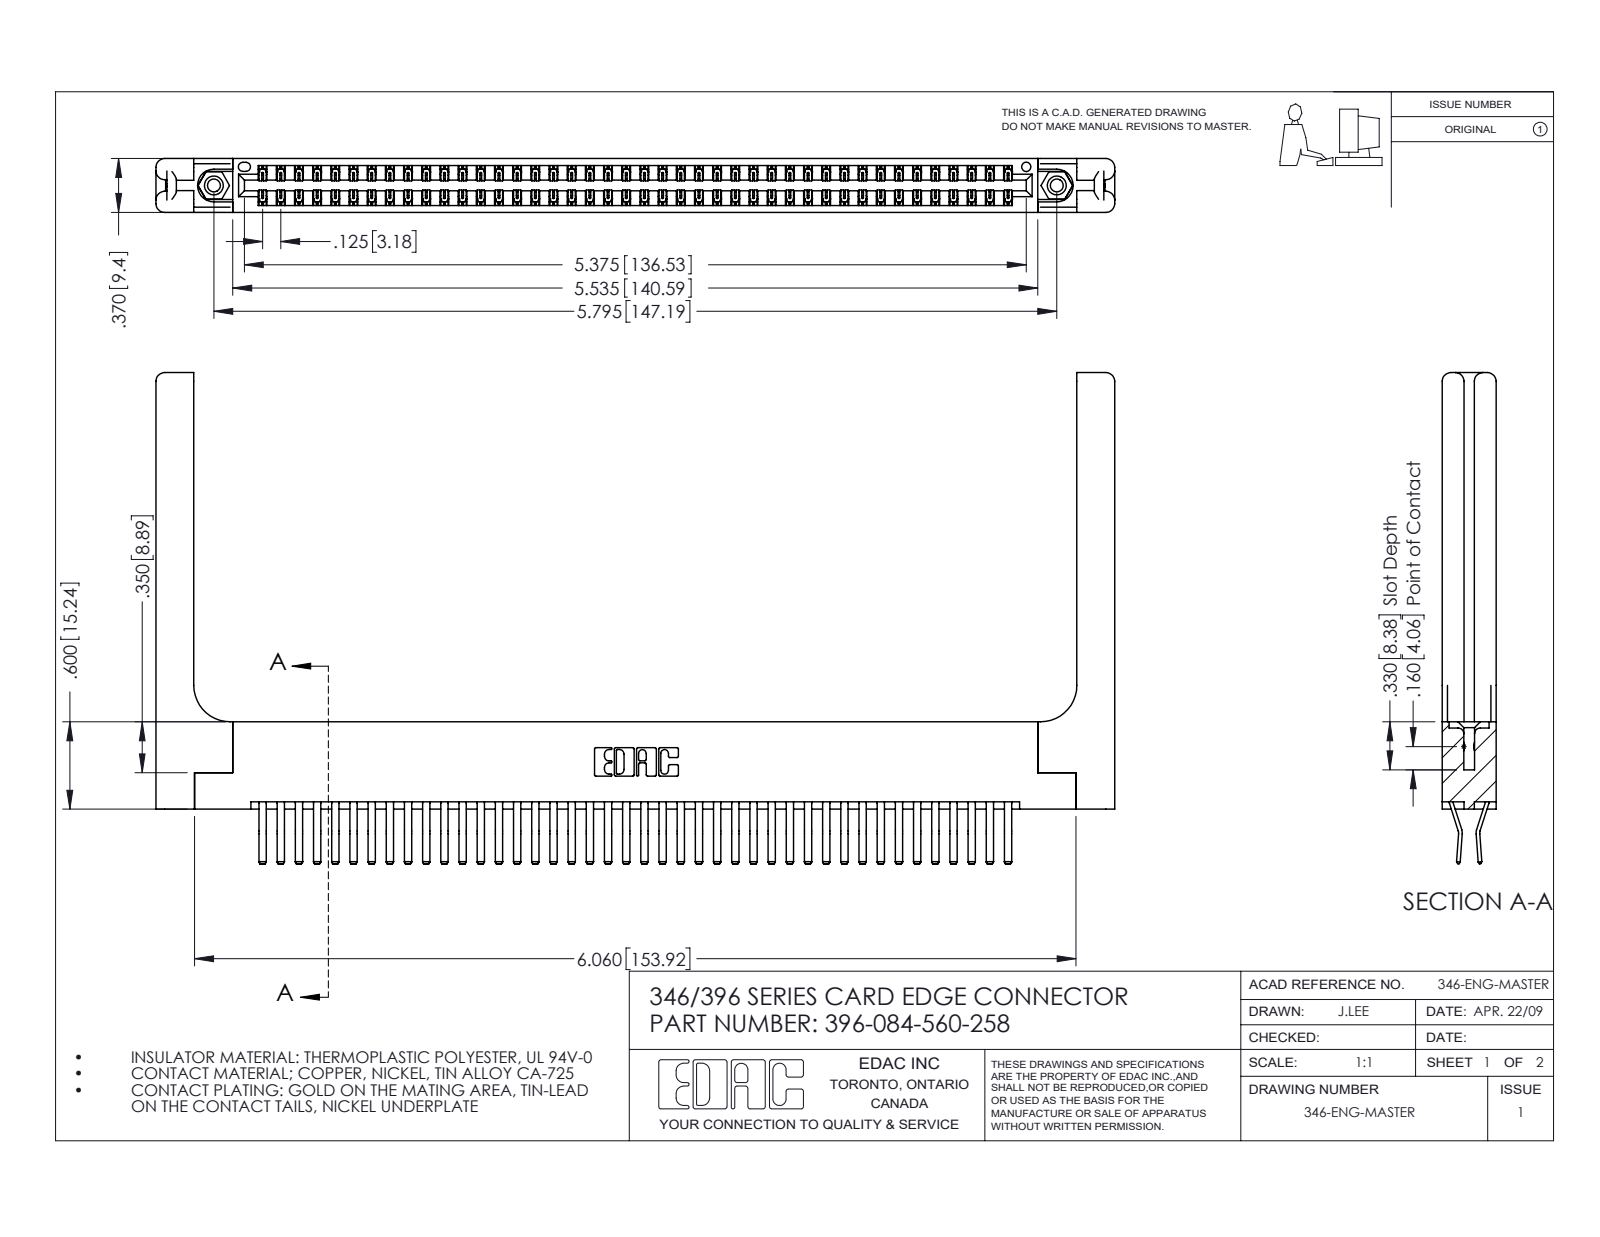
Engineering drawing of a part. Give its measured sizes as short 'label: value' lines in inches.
name: 346 Part_Flush Mounting Lugs - 0.156 Dia-TH; 345-250-001_345-250-001-102; 345-292-001_560 Tail; 346-220-058_345-220-058 (+1 more)
written by: SolidWorks 2016 (CONFIG_CONTROL_DESIGN)
unit: in
bodies: 89 solids, 4914 faces (3164 planar, 1690 cylindrical, 60 other)
size: 6.591 × 3.375 × 0.37
volume: 1.487 in³; area: 45.94 in²
holes: 2× ⌀0.089, 2× ⌀0.125, 2× ⌀0.156, 1× ⌀0.064
bosses: 2× ⌀0.155
rounds: 126× R0.006, 22× R0.01, 16× R0.06, 6× R0.007, 6× R0.031, 3× R0.026, 2× R0.01, 2× R0.014
face distances: 0.37, 0.048, 0.322, 0.072, 0.025, 0.148, 0.15, 0.25, 0.298, 0.275
hole spacings: 0.246, 5.586, 5.795
